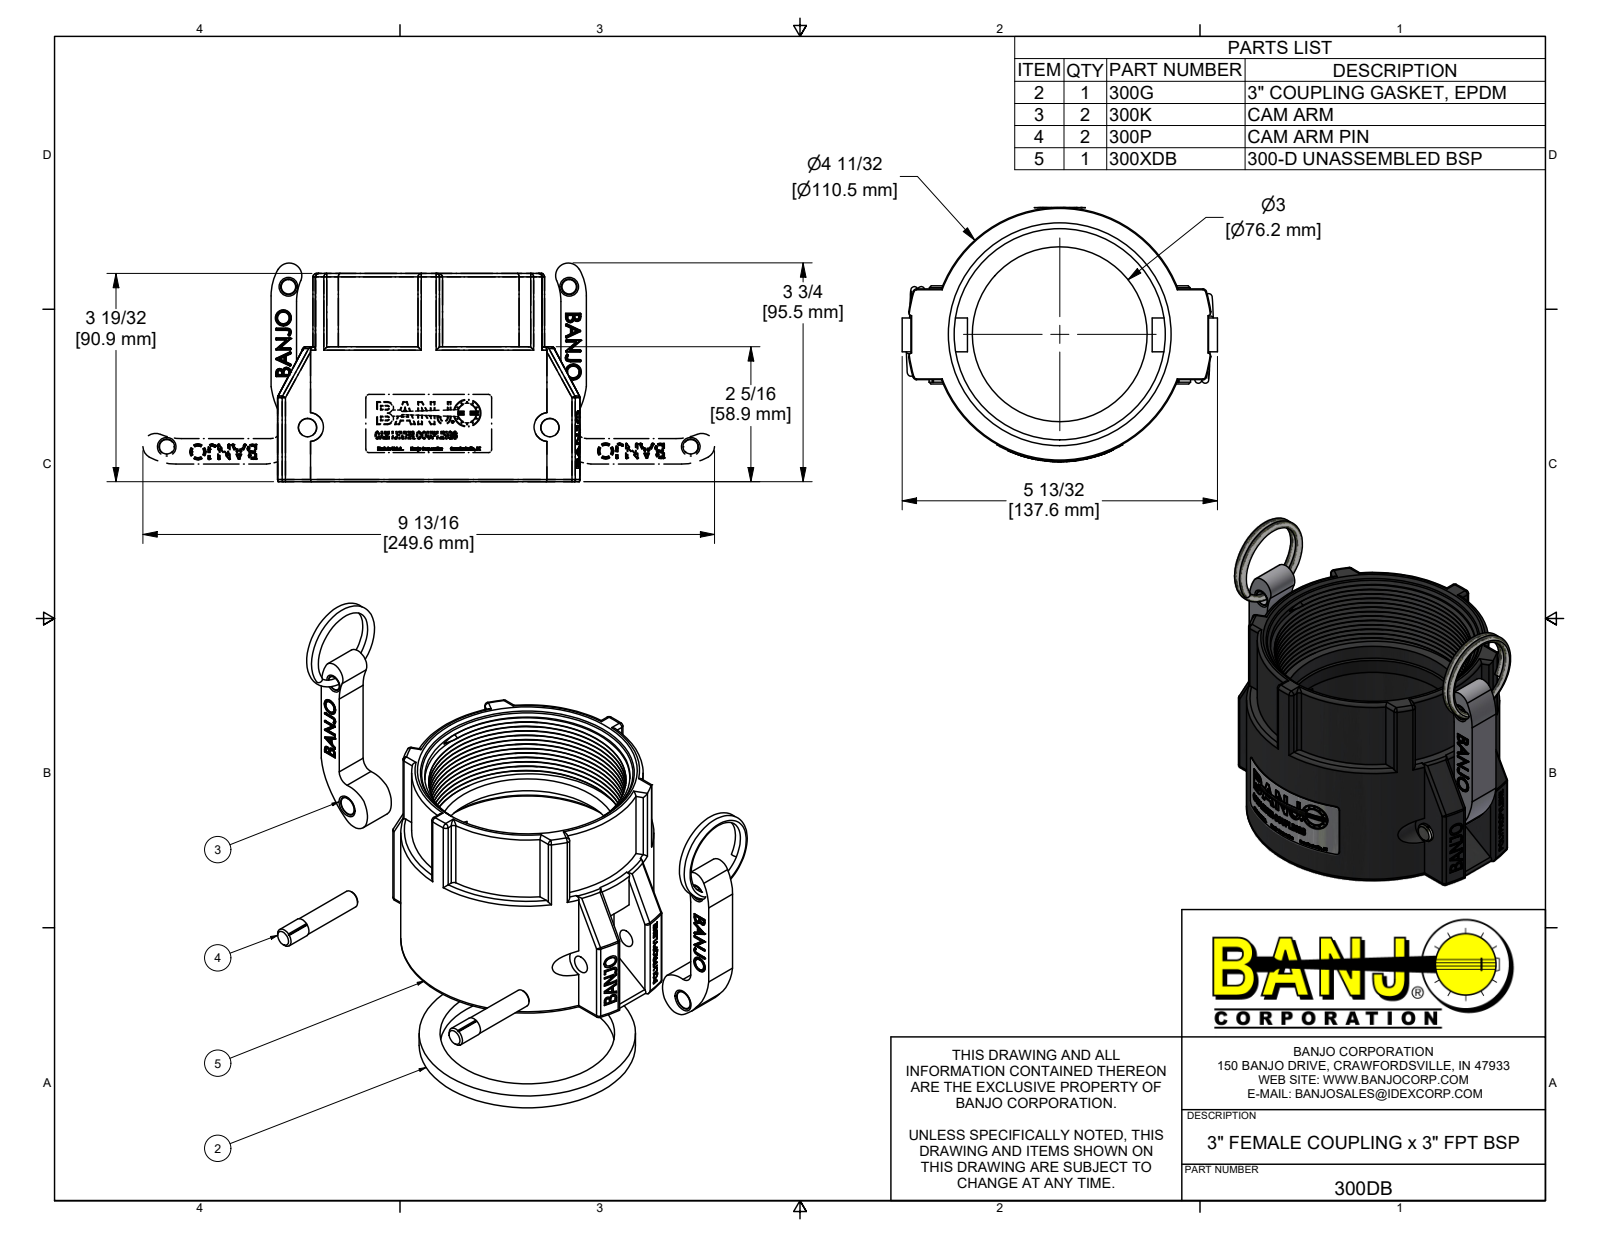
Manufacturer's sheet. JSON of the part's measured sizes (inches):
{"part_name": "300DB; 300XDB; VL1012; 300K (+5 more)", "step_written_by": "Autodesk Inventor 2022 (AUTOMOTIVE_DESIGN)", "units": "inches", "bodies": {"solids": 10, "faces": 3351, "planar": 1316, "cylindrical": 638, "other": 1397}, "overall_size": [5.419, 4.769, 4.369], "volume_in3": 19.42, "surface_area_in2": 166.9, "round_holes": [[0.25, 2], [0.313, 2], [0.319, 2], [0.318, 1], [0.449, 1], [3, 1], [3.06, 1], [3.63, 1], [3.8, 1]], "round_bosses_or_shafts": [[0.325, 2], [0.311, 2], [4.35, 1], [3.719, 1], [0.473, 1]], "partial_cylinders_radius": [[0.006, 234], [0.06, 41], [0.005, 34], [0.929, 4], [0.028, 2], [0.039, 2], [0.05, 2], [0.093, 2]], "face_to_face_distances": [2.045, 0.25, 1.795, 0.275, 0.46, 1.1, 0.525, 2.32, 0.58, 0.62], "hole_center_spacings": [2.442, 5.106, 1.445, 2.755, 2.789, 3.761, 4.167, 4.824]}
